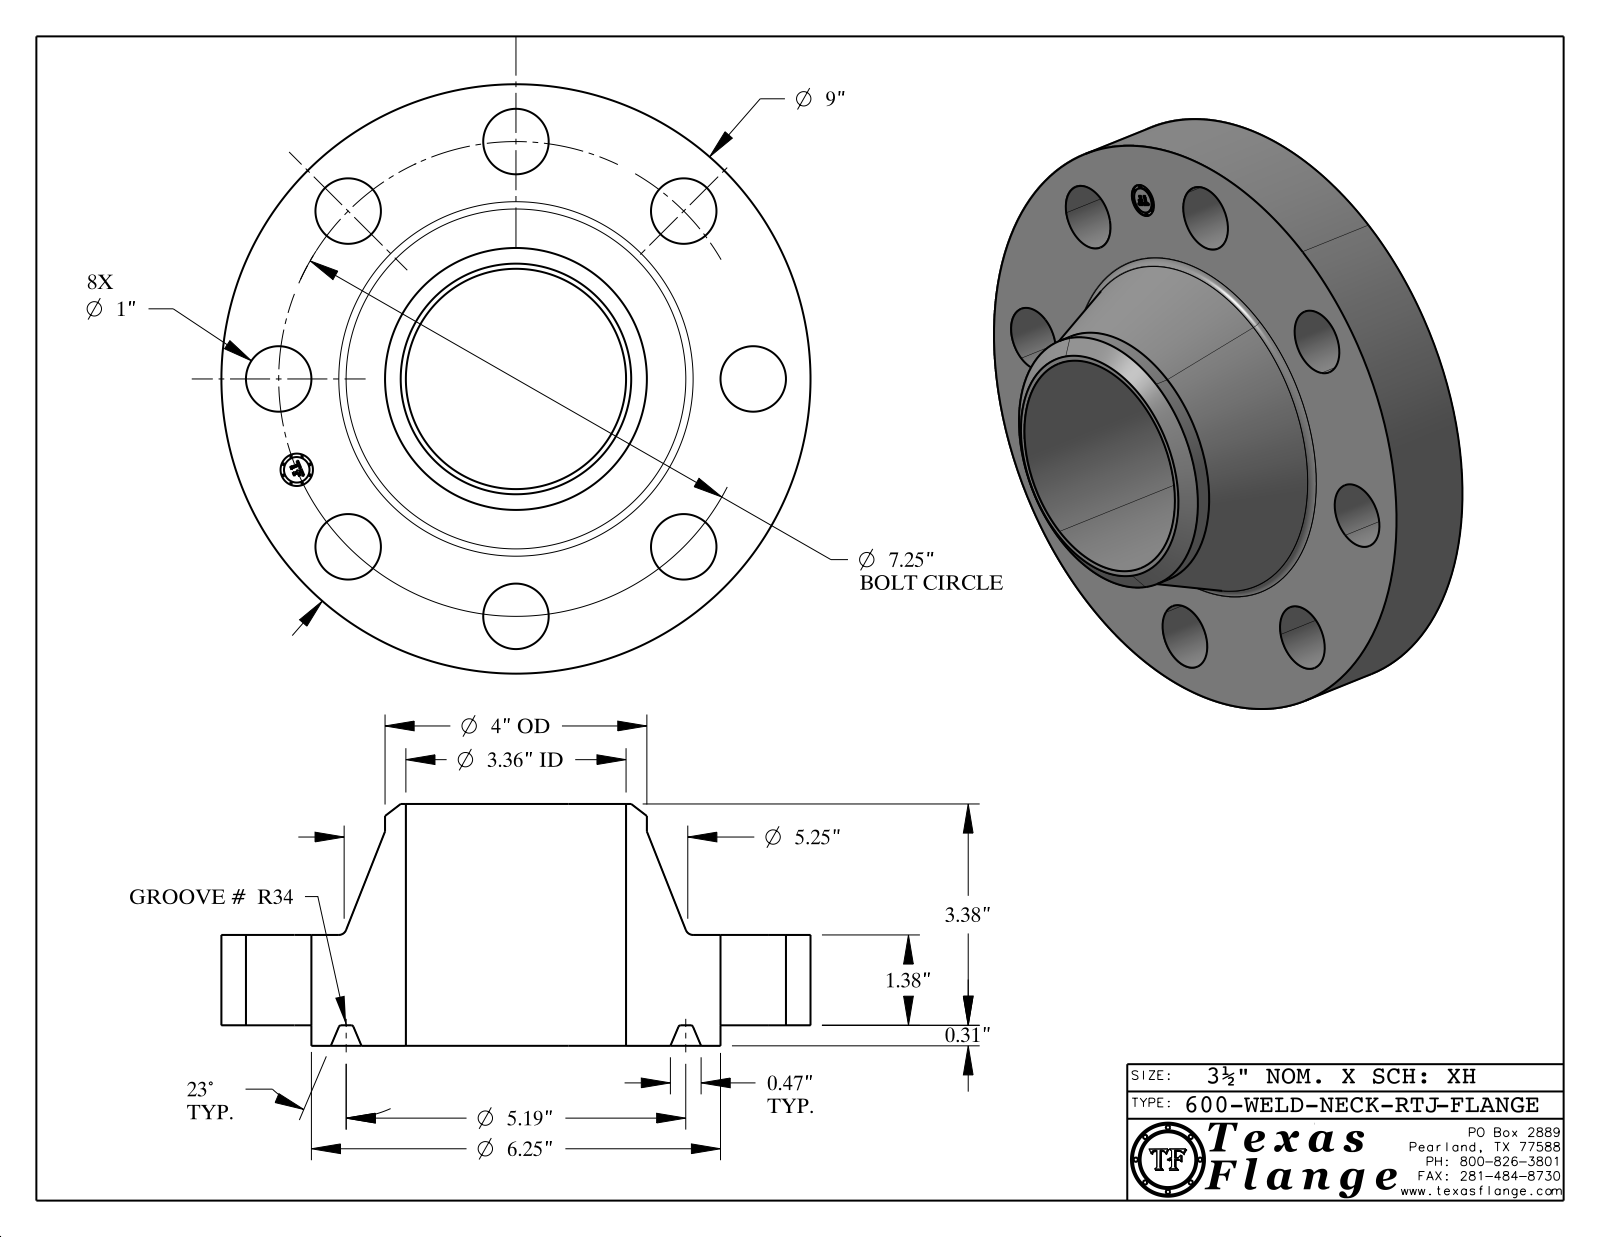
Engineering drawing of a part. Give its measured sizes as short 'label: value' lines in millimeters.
name: 600-WELD-NECK-RTJ
written by: CATIA V5 STEP AP214 (AUTOMOTIVE_DESIGN)
unit: mm
bodies: 1 solid, 429 faces (371 planar, 44 cylindrical, 14 other)
size: 228.6 × 228.6 × 93.8
volume: 1 408 000 mm³; area: 155 700 mm²
holes: 8× ⌀25.4, 1× ⌀12.6, 1× ⌀85.4
bosses: 8× ⌀0.8, 1× ⌀228.6, 1× ⌀158.8, 1× ⌀101.6, 1× ⌀9.9
face distances: 35.1, 8, 43, 93.8, 85.9, 50.8, 42.6, 34.7, 0.4, 51.2
hole spacings: 92.1, 70.5, 130.2, 170.1, 184.2, 35.9, 180.6, 102.3
